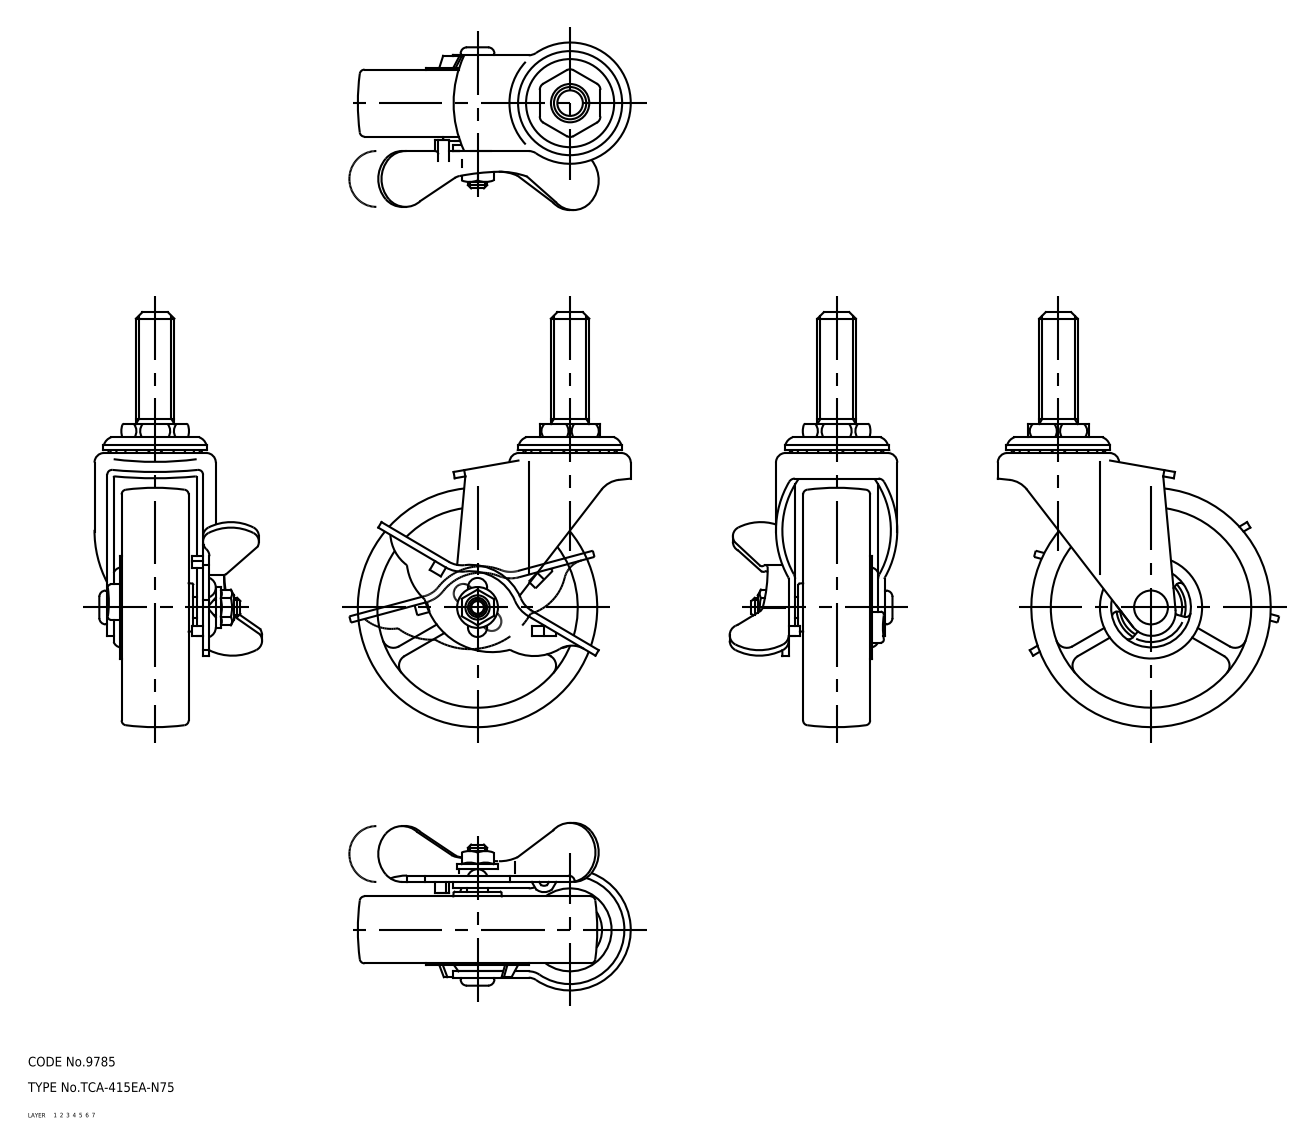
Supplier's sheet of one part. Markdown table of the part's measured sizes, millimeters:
| quantity | value |
| --- | --- |
| part name | wheel; mounting plate; main shaft; lever (+2 more) |
| STEP written by | CADfix (AUTOMOTIVE_DESIGN) |
| units | millimeters |
| bodies | 6 solids, 479 faces (0 planar, 0 cylindrical, 479 other) |
| overall size | 130 × 85.5 × 52.45 |
| volume | 91 987 mm³ |
| surface area | 40 158 mm² |
